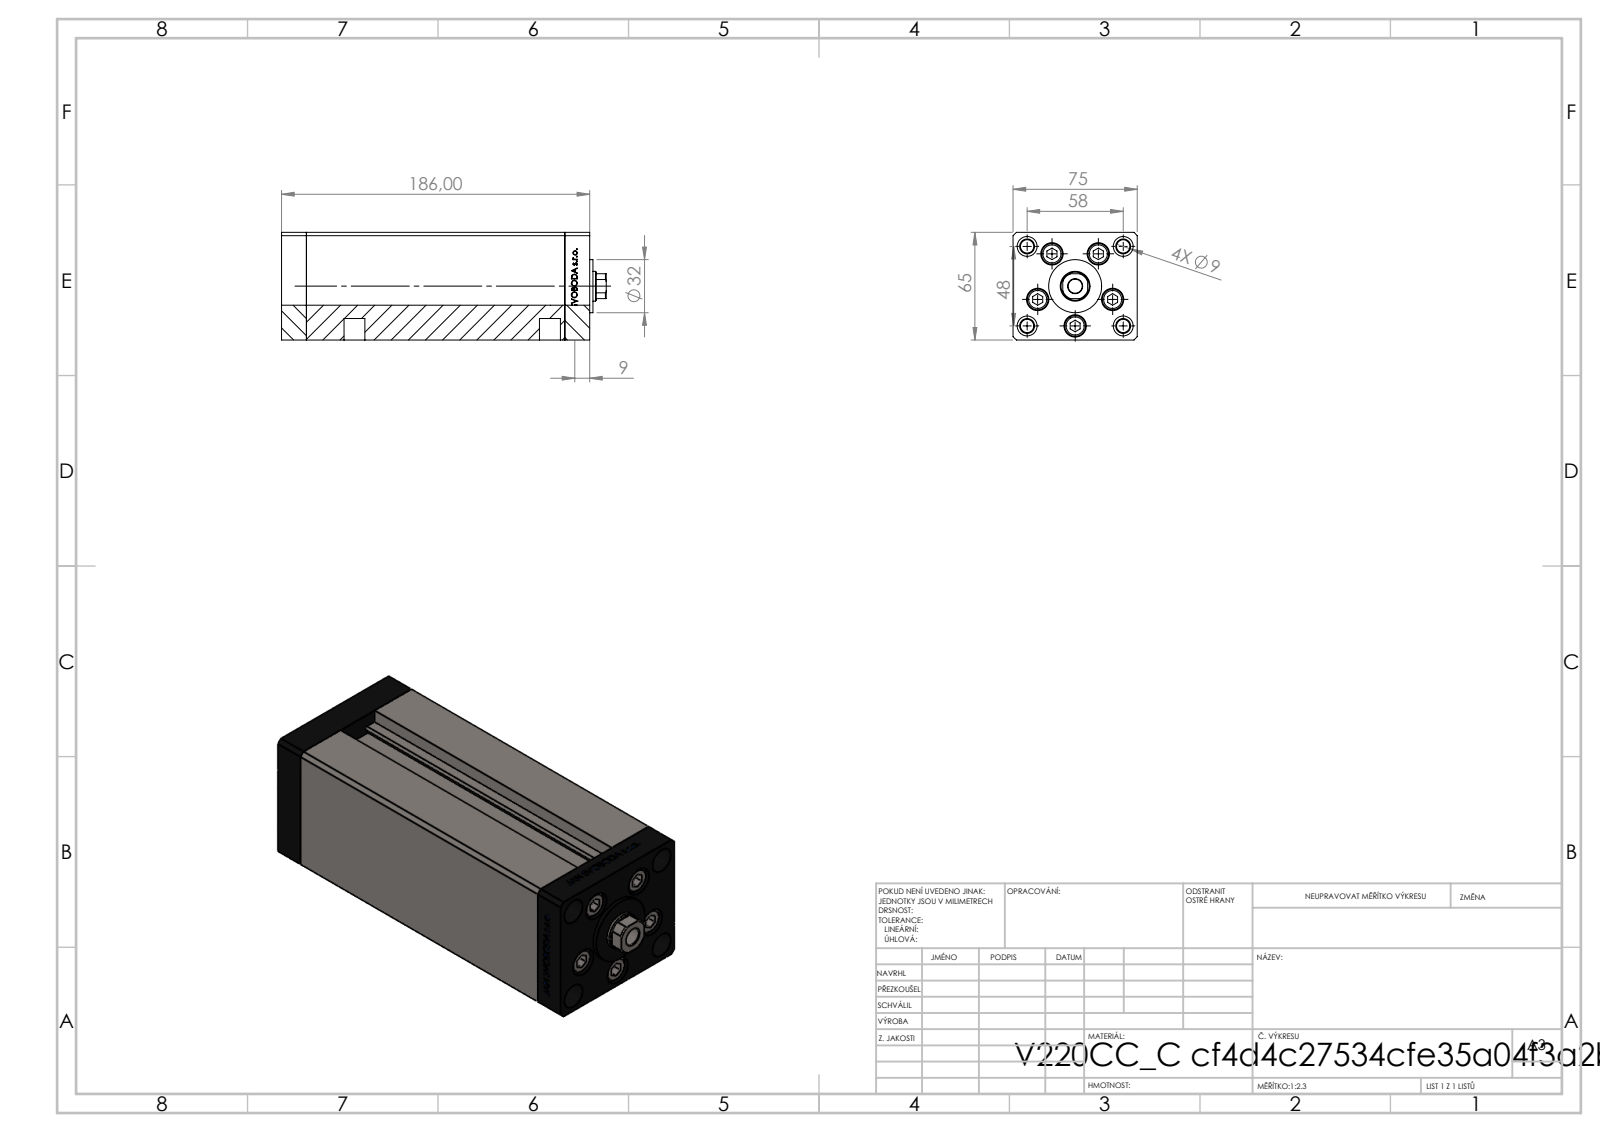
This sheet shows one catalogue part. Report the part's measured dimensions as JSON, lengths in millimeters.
{"part_name": "V220C_C MIDDLE; V220C FRONT; V220C BACK_C; ALLEN BOLT (+1 more)", "step_written_by": "SolidWorks 2019 (CONFIG_CONTROL_DESIGN)", "units": "millimeters", "bodies": {"solids": 13, "faces": 1179, "planar": 542, "cylindrical": 175, "other": 462}, "overall_size": [196, 75, 65], "volume_mm3": 754279, "surface_area_mm2": 155117, "round_holes": [[9, 9], [13.5, 5], [2, 4], [8, 4], [12, 4], [13.16, 4], [8.5, 1], [12.5, 1], [18, 1]], "round_bosses_or_shafts": [[8, 5], [12.5, 4], [32, 1]], "partial_cylinders_radius": [[0.93, 2], [8.5, 1]], "face_to_face_distances": [75, 65, 15, 156, 171, 186, 28, 13, 54.5, 10.5], "hole_center_spacings": [24, 37.64, 15.67, 17.22, 27.71, 28.83, 29, 32.63]}
